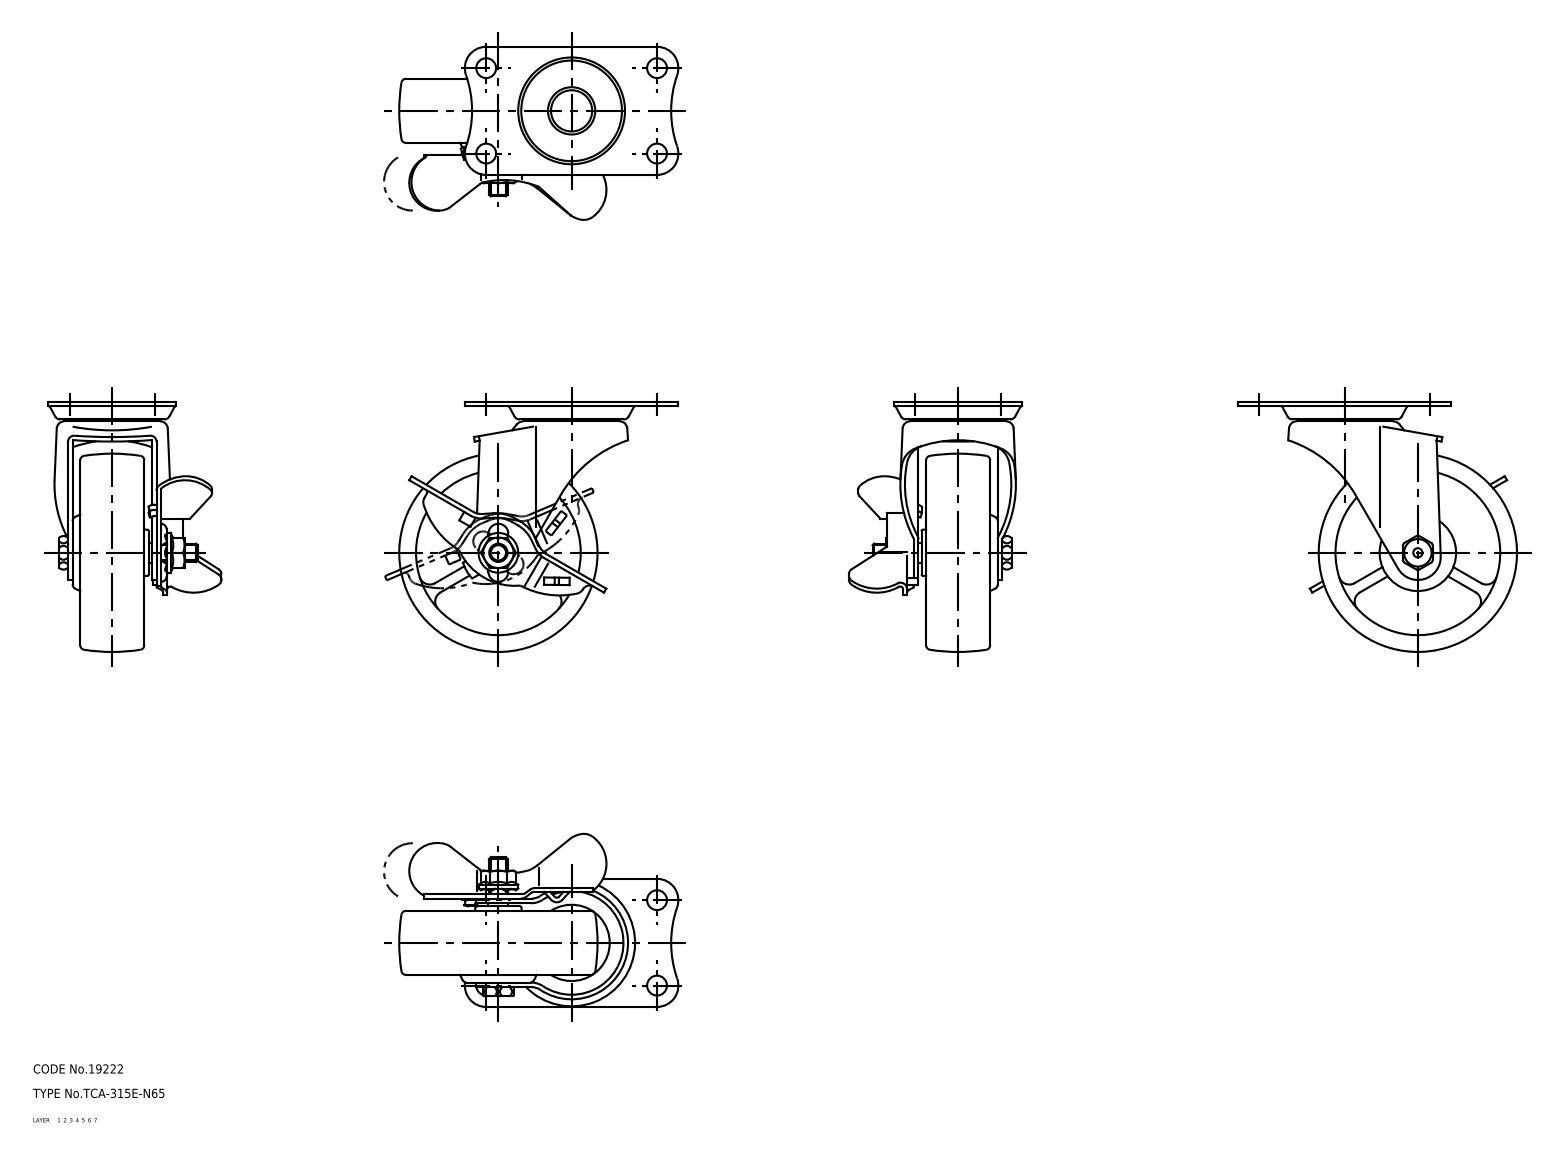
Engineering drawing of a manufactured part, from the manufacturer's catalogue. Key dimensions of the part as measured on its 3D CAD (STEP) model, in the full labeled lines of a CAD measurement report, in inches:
Part name (STEP PRODUCT): axle; wheel; mounting plate; main shaft (+2 more)
STEP written by: CADfix (AUTOMOTIVE_DESIGN)
Units: inches
Bodies: 8 solids, 602 faces (0 planar, 0 cylindrical, 602 other)
Overall size (bounding box): 3.602 × 3.228 × 2.234
Volume: 4.172 in³ · Surface area: 58.28 in²
